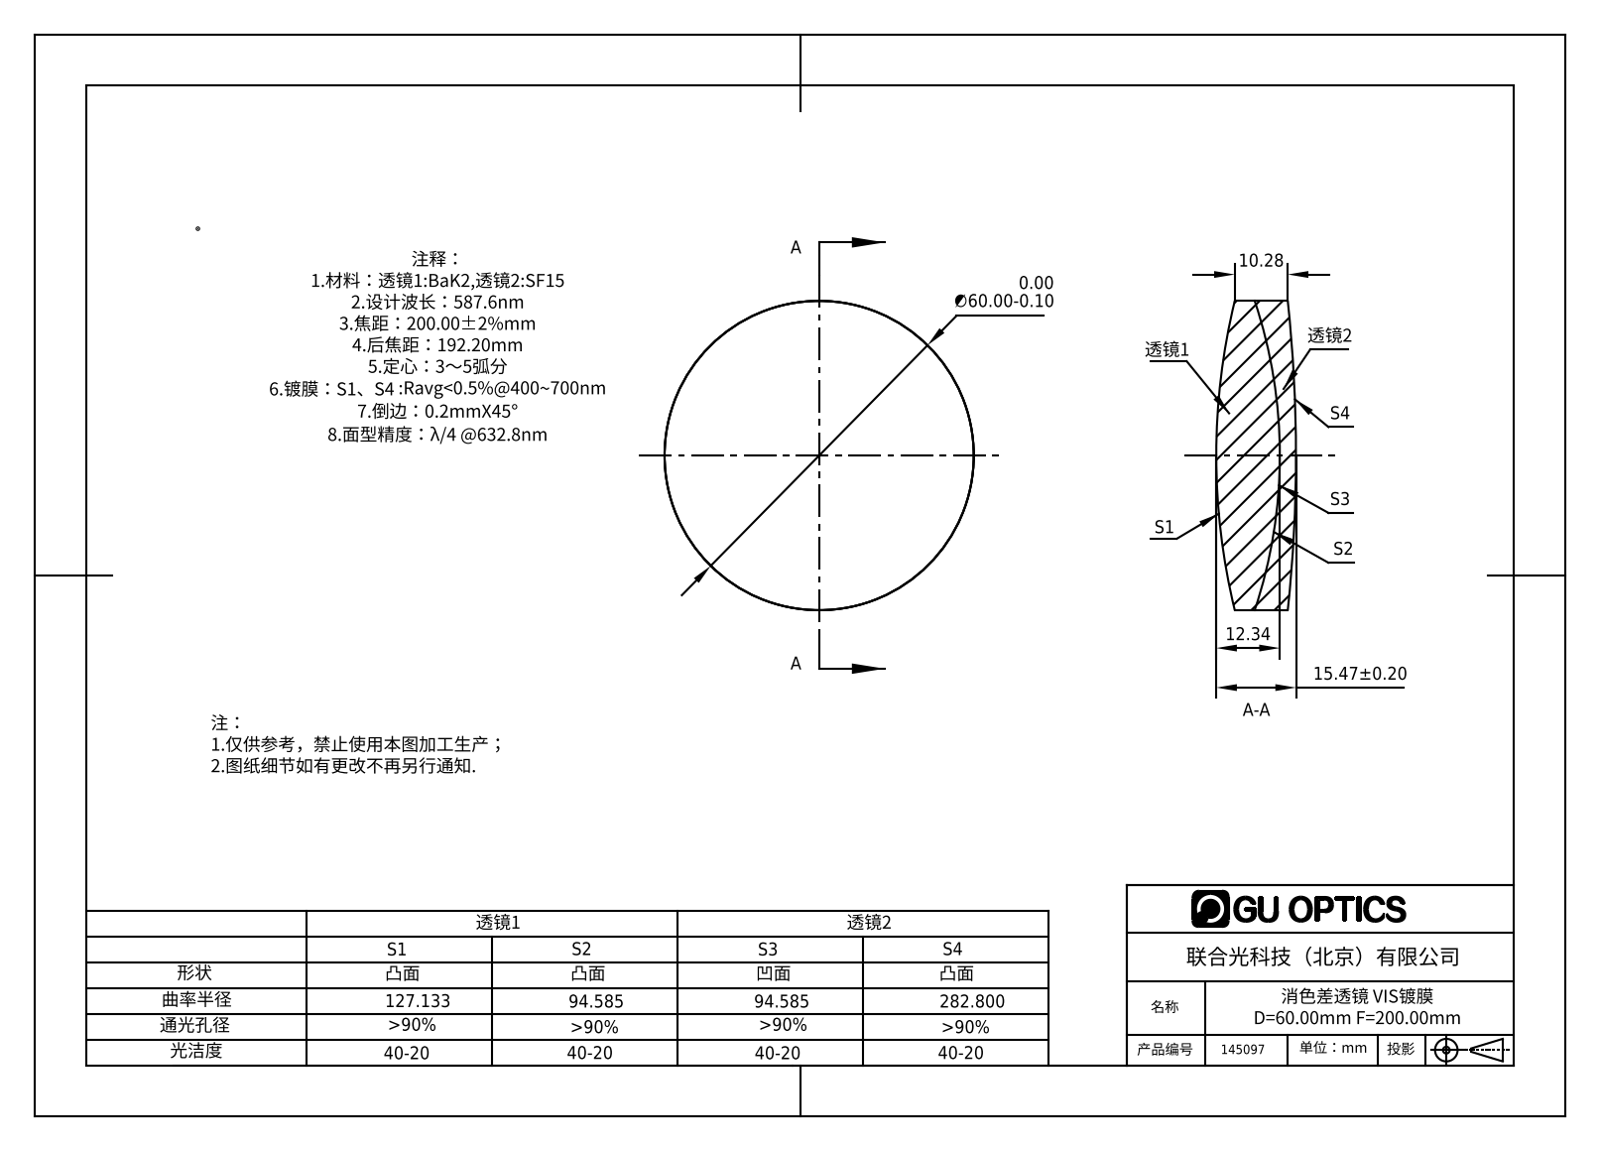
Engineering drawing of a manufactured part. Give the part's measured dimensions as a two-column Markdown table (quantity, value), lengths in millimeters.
| quantity | value |
| --- | --- |
| part name | 145097 |
| STEP written by | SolidWorks 2016 (AUTOMOTIVE_DESIGN) |
| units | millimeters |
| bodies | 2 solids, 12 faces (0 planar, 4 cylindrical, 8 other) |
| overall size | 60 × 60 × 15.47 |
| volume | 36 435 mm³ |
| surface area | 13 447 mm² |
| round bosses / shafts (diameter × count) | 60 × 1 |
